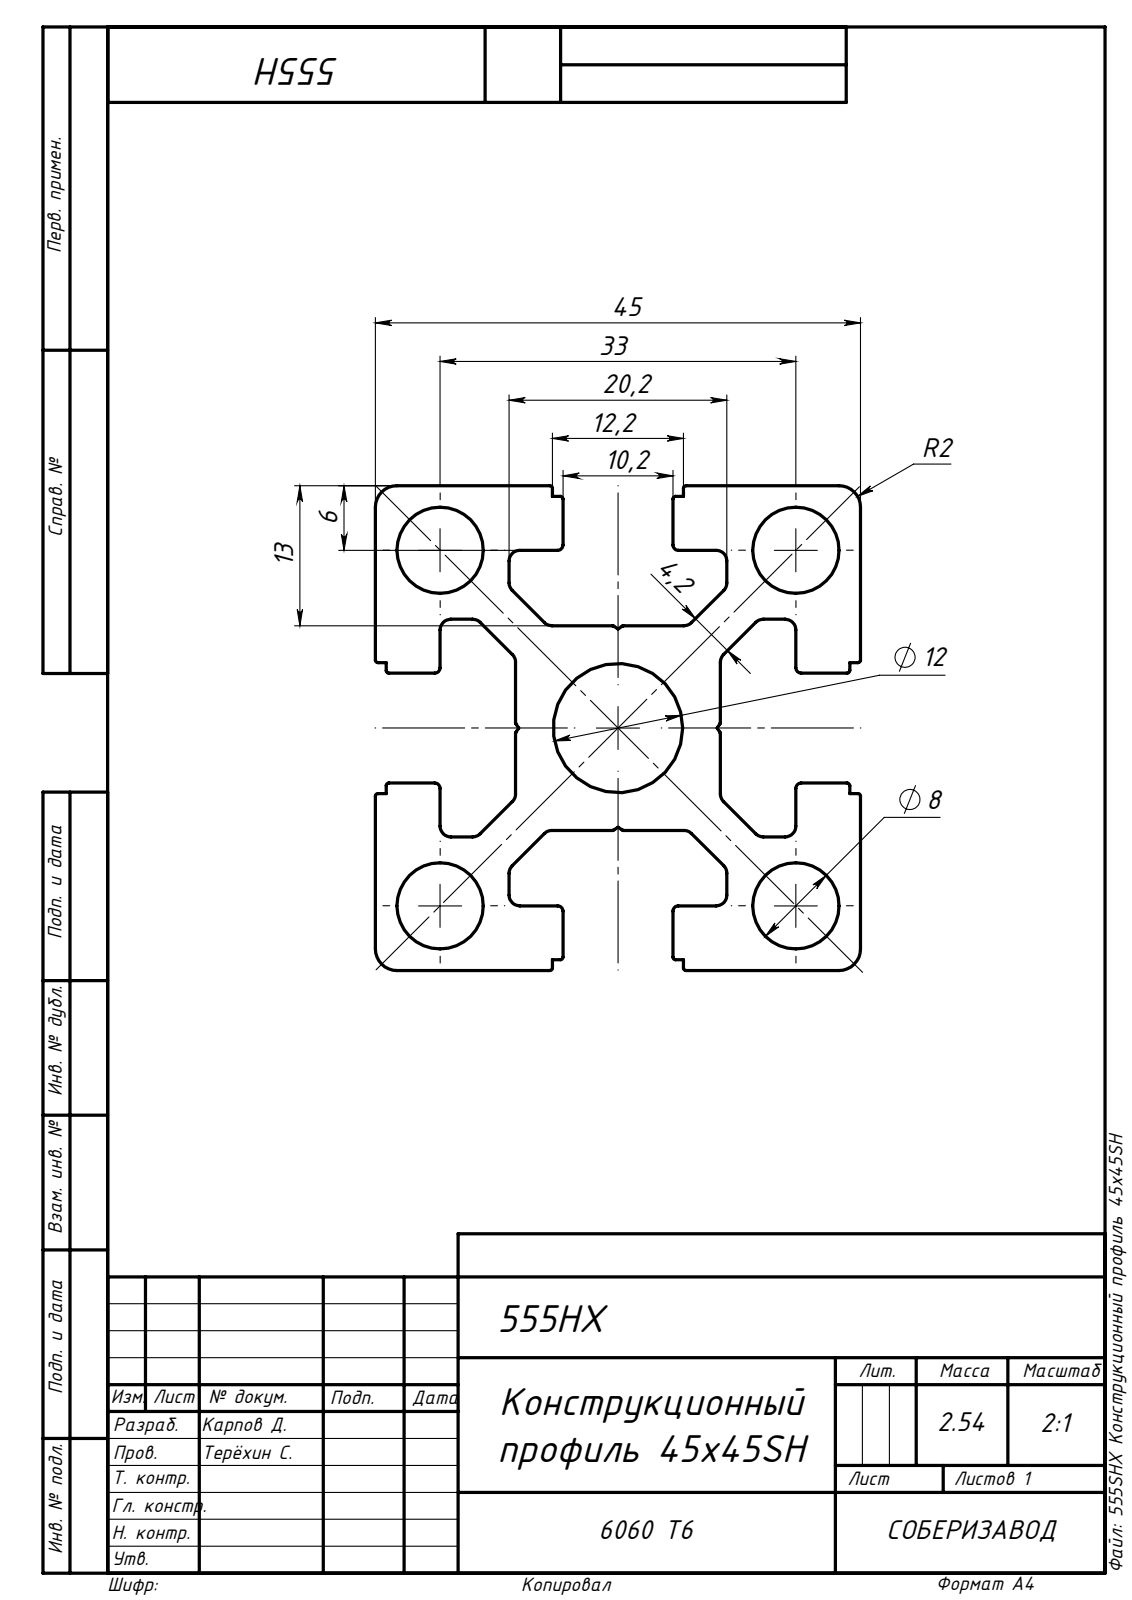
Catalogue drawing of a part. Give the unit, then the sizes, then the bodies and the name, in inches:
Units: inches
Overall size (bounding box): 39.37 × 1.772 × 1.772
Round holes (diameter × count): ⌀0.315 ×4, ⌀0.472 ×1
Partial cylindrical surfaces — rounded edges, fillets, slot ends (radius × count): R0.01 ×24, R0.039 ×24, R0.02 ×8, R0.079 ×4
Main face-to-face distances: 1.772, 0.512, 1.26, 0.685, 1.087, 0.173, 0.575, 0.449, 0.236, 1.535
Hole centre spacings: 0.919, 1.299, 1.837
Volume: 57.43 in³ · Surface area: 739.5 in²
Bodies: 1 solid, 152 faces (74 planar, 78 cylindrical, 0 other)
STEP written by: SolidWorks 2019 (AUTOMOTIVE_DESIGN)
